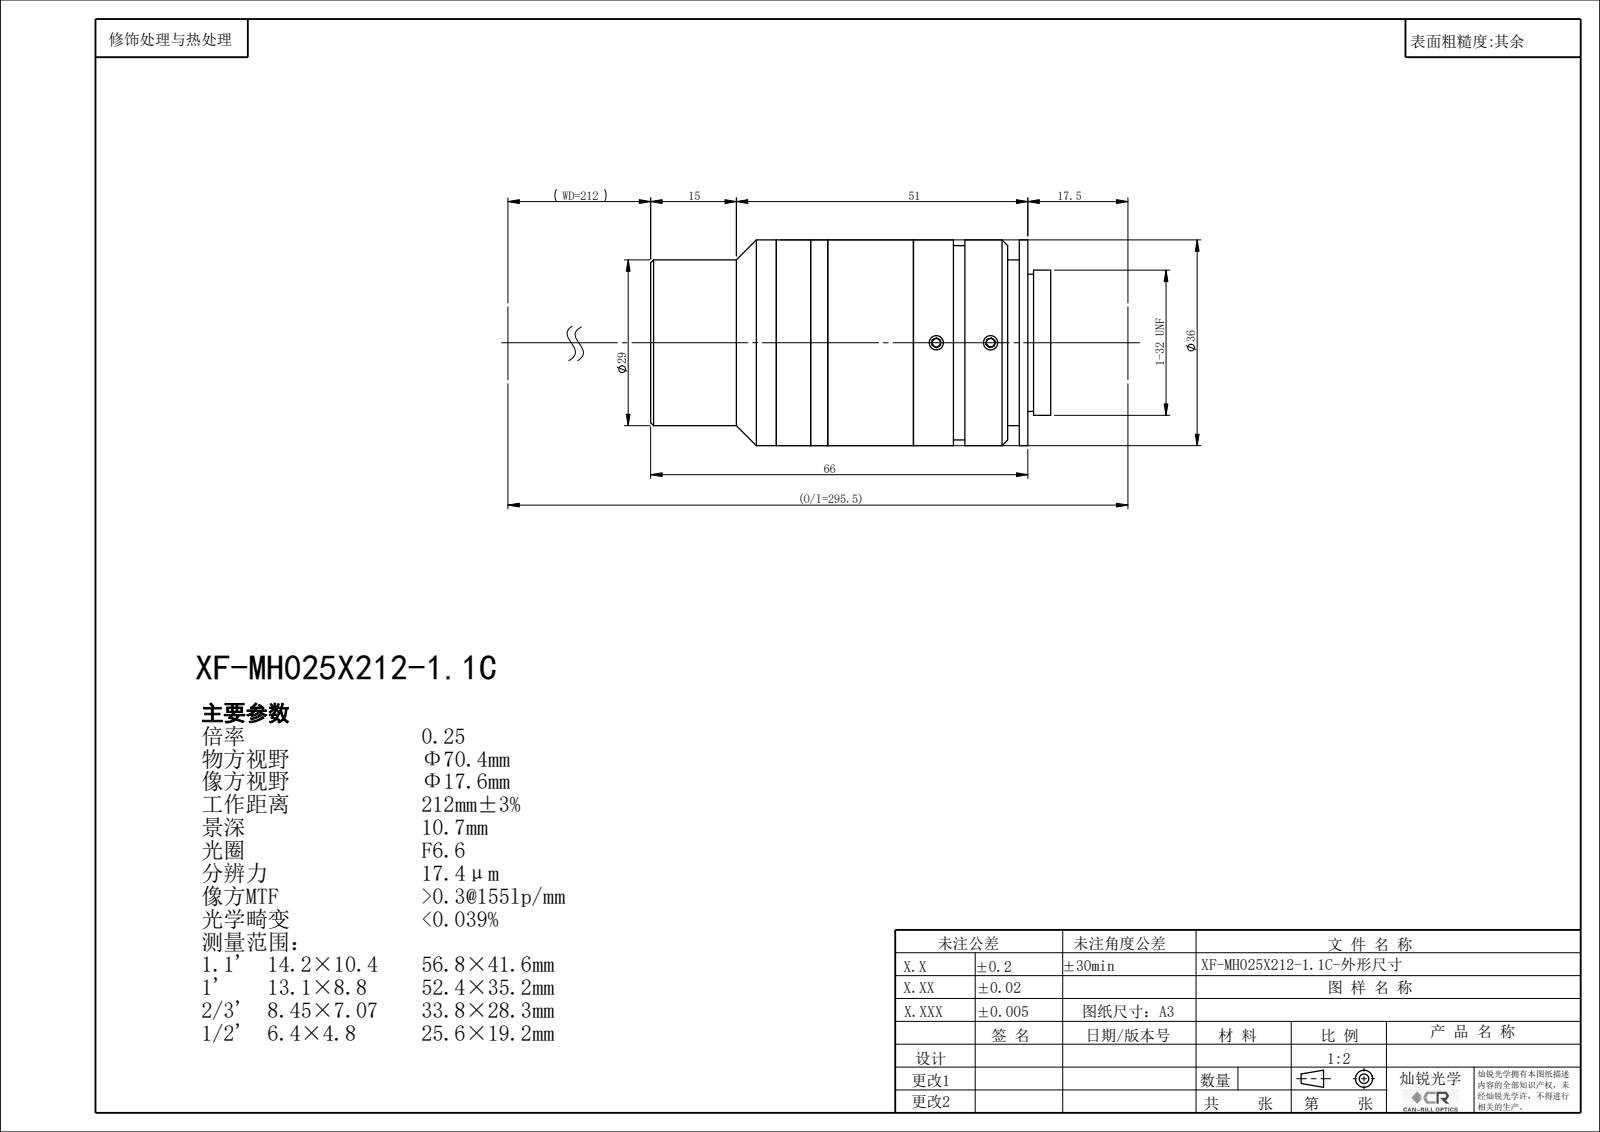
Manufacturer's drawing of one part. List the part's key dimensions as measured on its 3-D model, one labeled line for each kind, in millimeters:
Part name (STEP PRODUCT): XF-MH025X212-1.1C
STEP written by: SolidWorks 2022 (CONFIG_CONTROL_DESIGN)
Units: millimetres
Bodies: 0 solids, 140 faces (67 planar, 50 cylindrical, 23 other)
Overall size (bounding box): 70.03 × 36 × 36
Round holes (diameter × count): ⌀2.5 ×6, ⌀20 ×1, ⌀22.4 ×1, ⌀24 ×1, ⌀24.9 ×1, ⌀26 ×1, ⌀26.4 ×1
Round bosses / shafts (diameter × count): ⌀36 ×1, ⌀34 ×1, ⌀29 ×1, ⌀25.4 ×1
Main face-to-face distances: 20.03, 1.5, 18.53, 15, 33.53, 35.03, 31.5, 16.5, 2.03, 3.53
Hole centre spacings: 9.5
